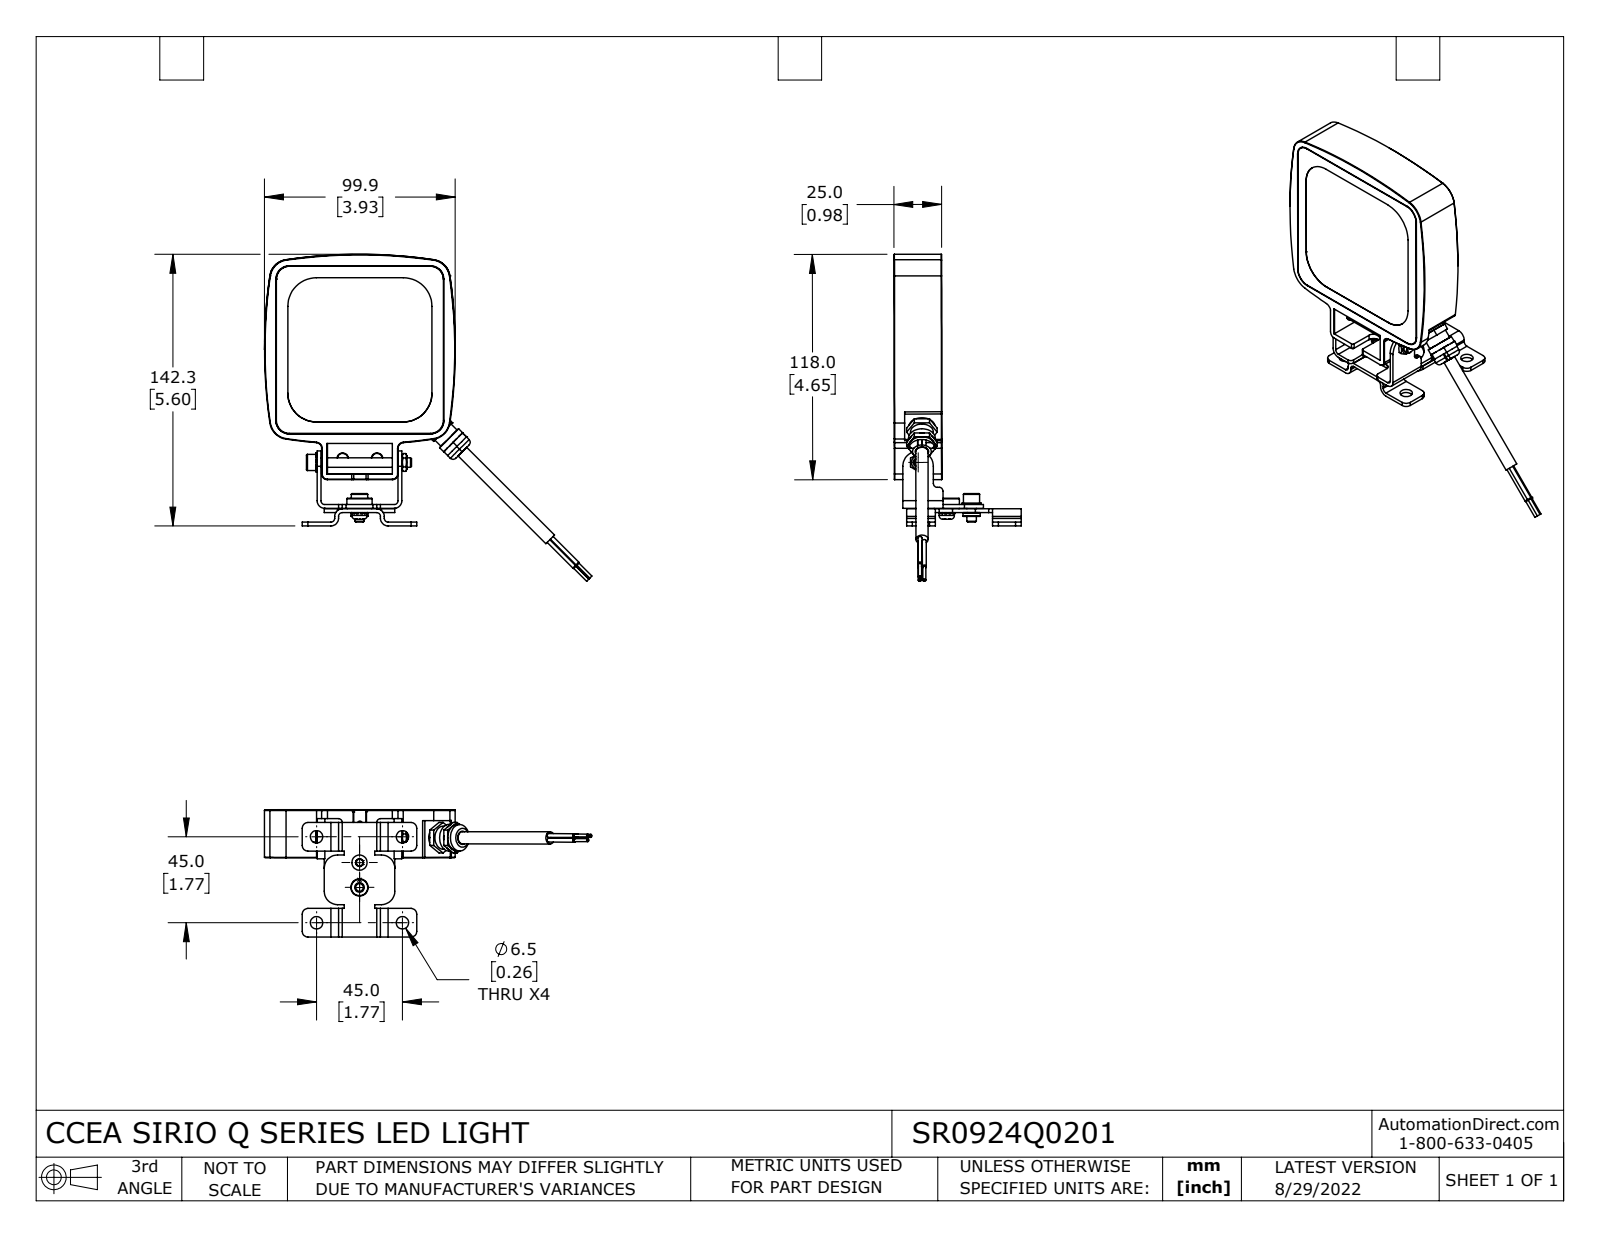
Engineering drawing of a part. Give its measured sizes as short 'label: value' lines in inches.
name: SR0924Q0201
written by: SolidWorks 2021 (CONFIG_CONTROL_DESIGN)
unit: in
bodies: 2 solids, 776 faces (331 planar, 324 cylindrical, 121 other)
size: 6.752 × 6.741 × 2.624
volume: 9.503 in³; area: 110.5 in²
holes: 4× ⌀0.097, 4× ⌀0.256, 3× ⌀0.043, 3× ⌀0.217, 2× ⌀0.276, 1× ⌀0.128, 1× ⌀0.169, 1× ⌀0.197, 1× ⌀0.209, 1× ⌀0.369, 1× ⌀0.531
bosses: 6× ⌀0.039, 4× ⌀0.082, 3× ⌀0.067, 3× ⌀0.063, 2× ⌀0.335, 2× ⌀0.197, 2× ⌀0.079, 1× ⌀0.551
rounds: 22× R0.005, 22× R0.006, 22× R0.079, 12× R0.118, 8× R0.276, 6× R0.157, 6× R0.394, 5× R0.197
face distances: 0.157, 0.823, 0.981, 0.079, 0.122, 0.701, 0.859, 0.161, 0.567, 0.724
hole spacings: 1.772, 1.033, 1.524, 2.506, 0.061, 0.061, 0.065, 0.066
